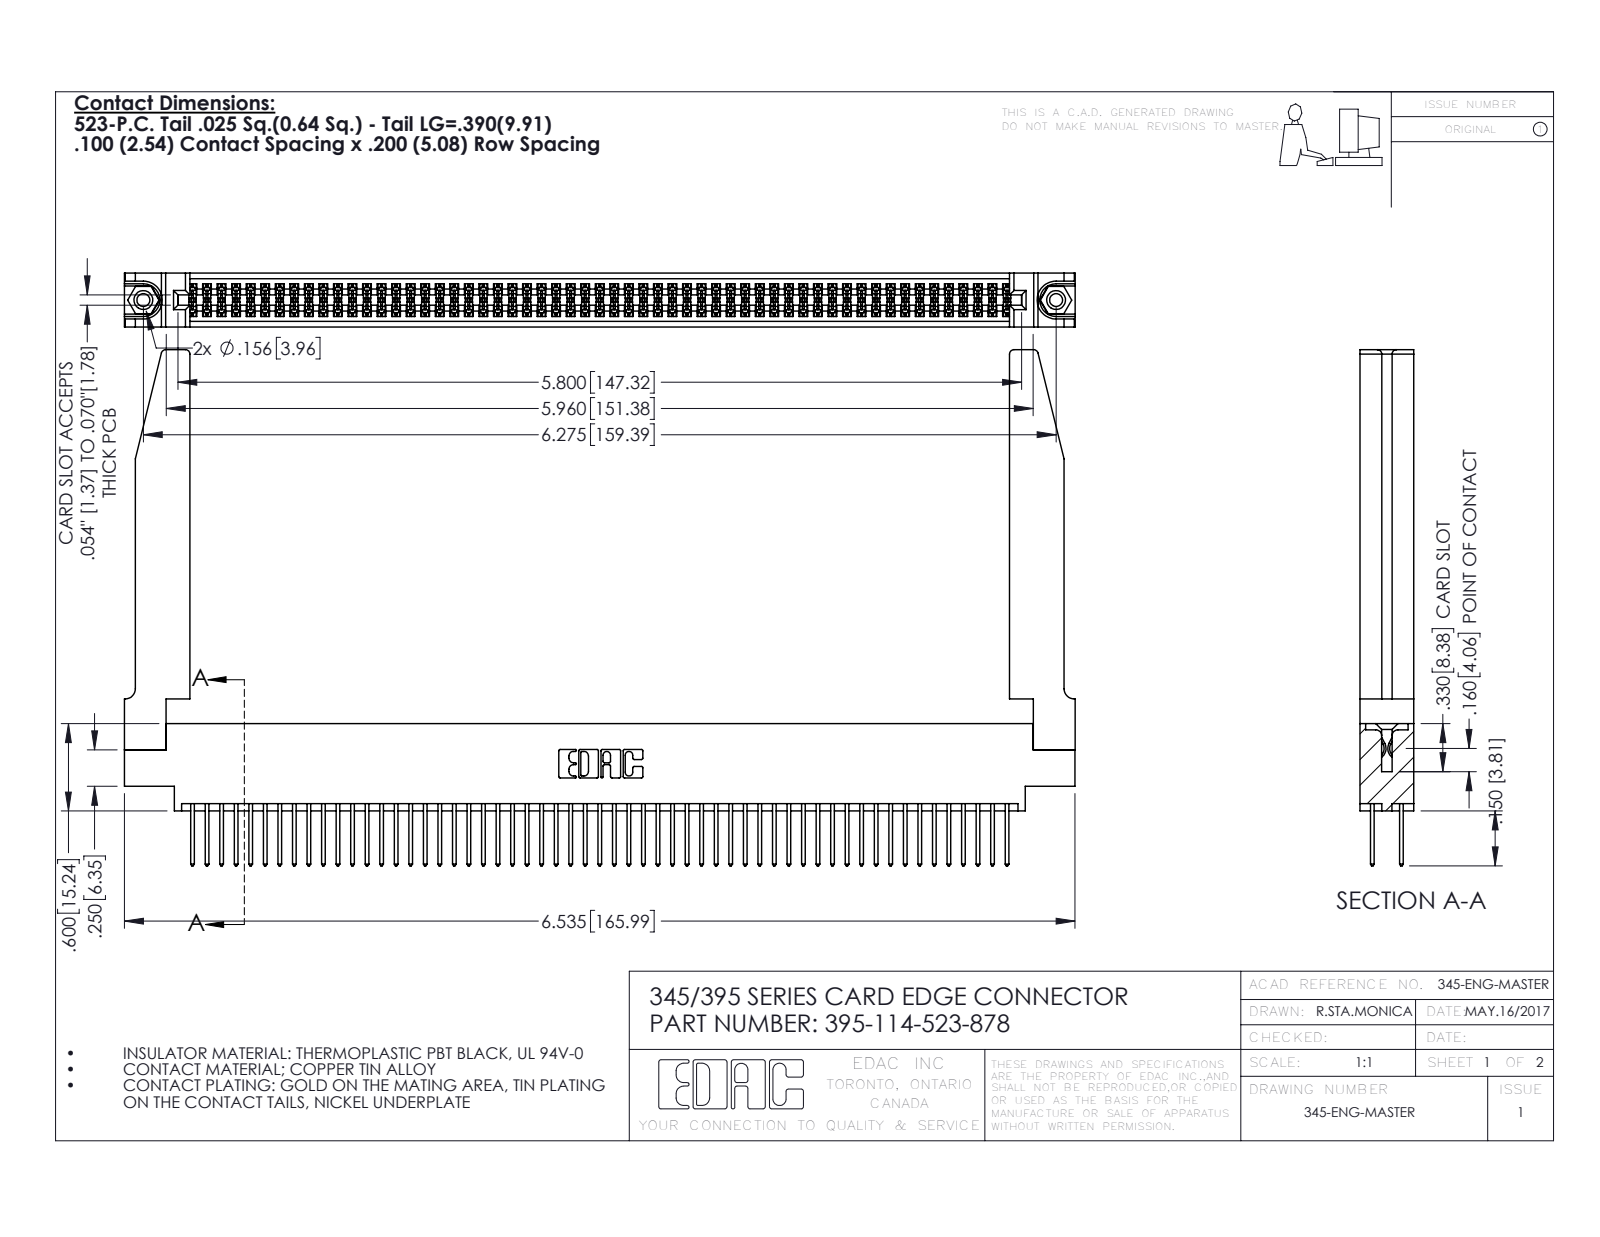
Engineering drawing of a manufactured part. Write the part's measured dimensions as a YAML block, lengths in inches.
part_name: "345-250-001_345-250-001-102; 345 Part_0.170 Offset - 0.156 Dia-TH; 345-292-001_345-293-123; 395-114-523-878 (+1 more)"
step_written_by: "SolidWorks 2016 (CONFIG_CONTROL_DESIGN)"
units: inches
bodies: {solids: 119, faces: 6064, planar: 3988, cylindrical: 2024, other: 52}
overall_size: [6.536, 3.547, 0.37]
volume: 1.474
surface_area: 50.44
round_holes:
  - {diameter: 0.089, count: 2}
  - {diameter: 0.125, count: 2}
  - {diameter: 0.156, count: 2}
  - {diameter: 0.064, count: 1}
round_bosses_or_shafts:
  - {diameter: 0.155, count: 2}
partial_cylinders:
  - {radius: 0.006, count: 171}
  - {radius: 0.01, count: 114}
  - {radius: 0.01, count: 22}
  - {radius: 0.03, count: 8}
  - {radius: 0.007, count: 6}
  - {radius: 0.031, count: 6}
  - {radius: 0.026, count: 3}
  - {radius: 0.014, count: 2}
face_to_face_distances: [0.072, 0.298, 0.37, 0.098, 0.272, 0.025, 0.2, 0.225, 0.175, 0.148]
hole_center_spacings: [0.27, 6.039, 6.275]
